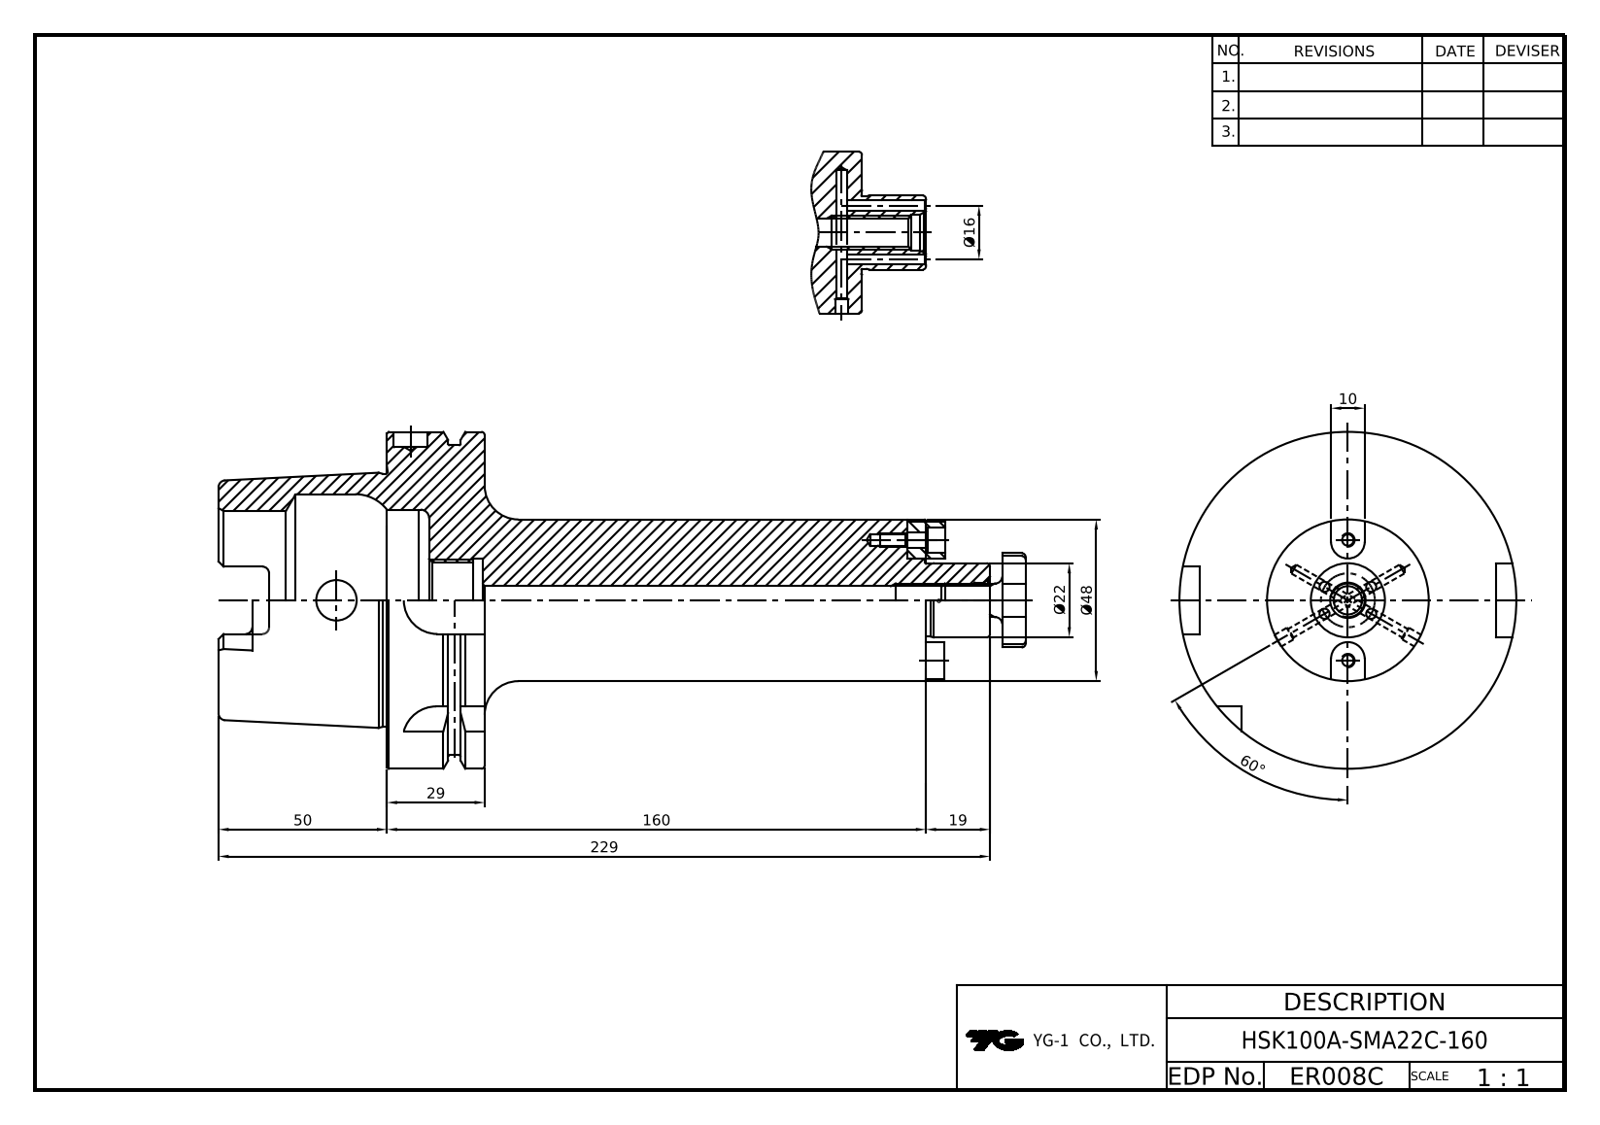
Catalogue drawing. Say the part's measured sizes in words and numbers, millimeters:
The part is named "LO-HSK100A-SMA22C-160; SMA22E-DRIVE KEY-SECO; HEX'' WRENCH BOLT-M4x0.7x12L; SMA22-COLLAR BOLT". Its 3-D file was written by "Autodesk Inventor 2025 (AP242_MANAGED_MODEL_BASED_3D_ENGINEERING_MIM_LF)". It is 6 solids with 205 faces: 85 planar, 61 cylindrical and 59 other. Overall it measures 186 by 100 by 100 millimeters. Its volume is 392 743 cubic millimeters and its surface area 69 388 square millimeters. Round holes: 4 of diameter 3, 2 of diameter 3.24, 2 of diameter 4.5, 2 of diameter 7.5, 1 of diameter 8.38, 1 of diameter 10, 1 of diameter 10.5, 1 of diameter 12, 1 of diameter 22.38, 1 of diameter 25, 1 of diameter 53, 1 of diameter 63. Round bosses or shafts: 2 of diameter 7, 2 of diameter 4, 1 of diameter 100, 1 of diameter 92, 1 of diameter 75.41, 1 of diameter 48, 1 of diameter 22, 1 of diameter 10. Partial cylindrical surfaces (rounded edges, fillets, slot ends): 6 of radius 2, 4 of radius 3, 4 of radius 4.88, 4 of radius 5, 4 of radius 10, 1 of radius 14. The main face-to-face distances are 29, 12.5, 16.5, 100, 87.5, 71, 62.5, 50, 79, 150. The hole center spacings are 8, 15.53, 22.97, 13.86, 16, 17.9, 35.8.
